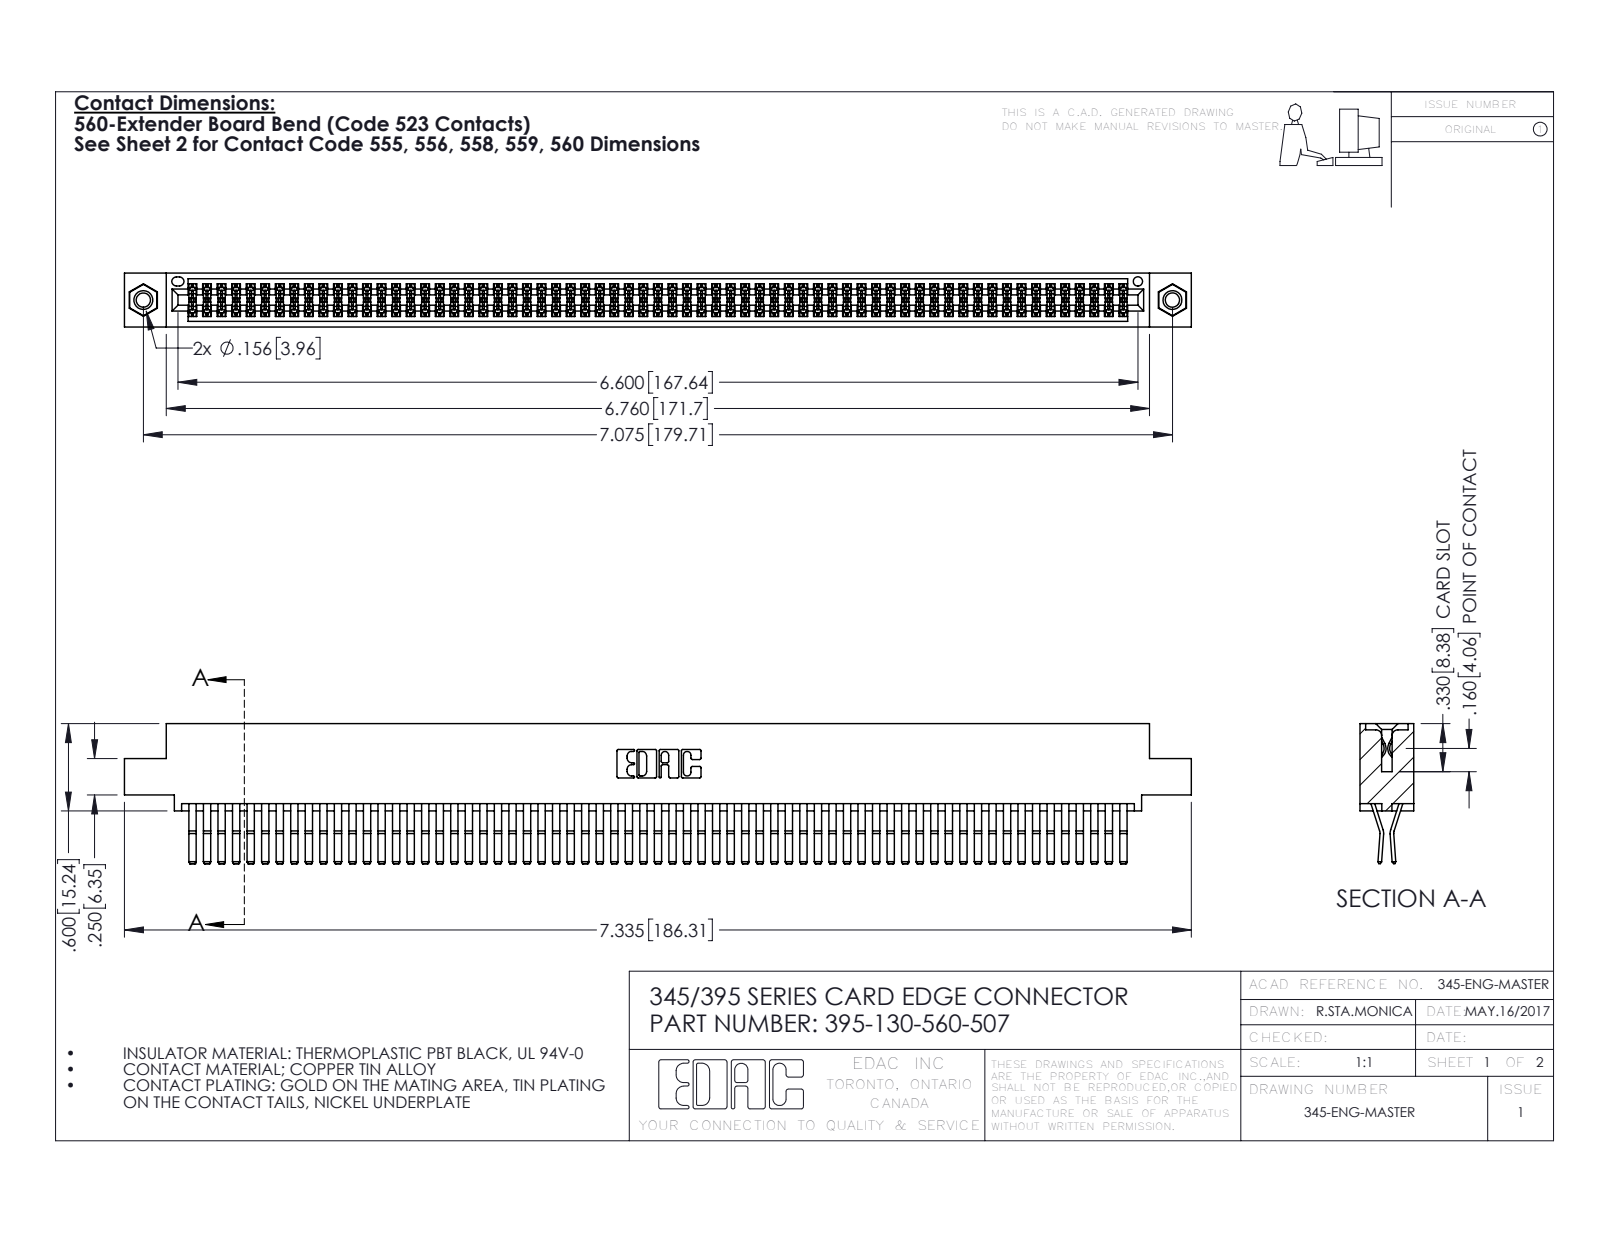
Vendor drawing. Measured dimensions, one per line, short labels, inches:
name: 345 Part_0.110 Offset - 0.156 Dia-TI; 345-250-001_345-250-005-103; 345-292-001_560 Tail; 395-130-560-507
written by: SolidWorks 2016 (CONFIG_CONTROL_DESIGN)
unit: in
bodies: 133 solids, 6950 faces (4406 planar, 2528 cylindrical, 16 other)
size: 7.335 × 0.962 × 0.37
volume: 1.164 in³; area: 47.98 in²
holes: 2× ⌀0.098, 2× ⌀0.125, 2× ⌀0.156, 1× ⌀0.064
bosses: 2× ⌀0.155
rounds: 196× R0.006, 22× R0.01, 6× R0.007, 6× R0.031, 3× R0.026, 2× R0.01, 2× R0.014, 2× R0.019
face distances: 0.025, 0.072, 0.298, 0.37, 0.2, 0.098, 0.272, 0.225, 0.175, 0.149
hole spacings: 0.27, 6.839, 7.075
